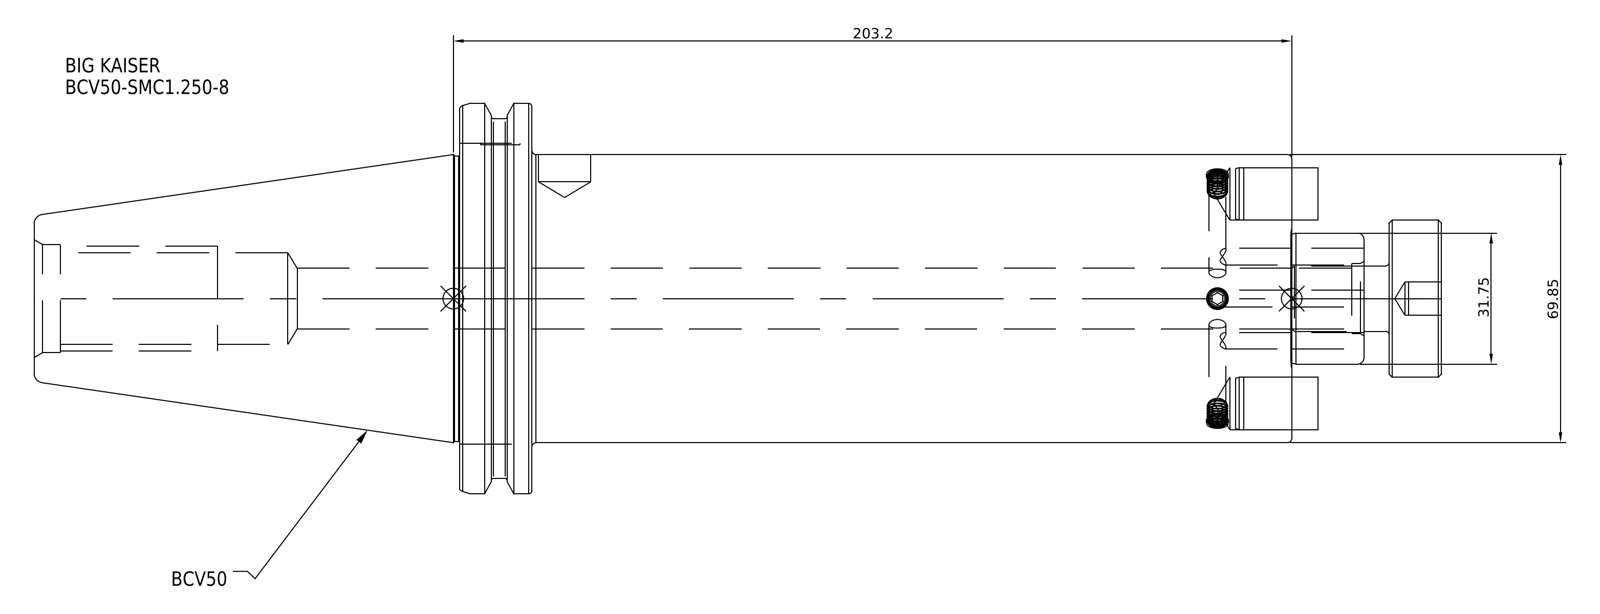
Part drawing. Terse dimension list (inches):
name: BCV50-SMC1_250-8
written by: SolidWorks 2021 (CONFIG_CONTROL_DESIGN)
unit: in
bodies: 1 solid, 35 faces (17 planar, 12 cylindrical, 6 other)
size: 12.252 × 3.875 × 3.875
volume: 64.75 in³; area: 133.7 in²
holes: 1× ⌀0.578
bosses: 1× ⌀3.875, 1× ⌀3.594, 1× ⌀2.75
face distances: 0.691, 7.25, 7.941, 12, 4.75, 4.059, 0.5, 0.252, 7.502, 8.193
